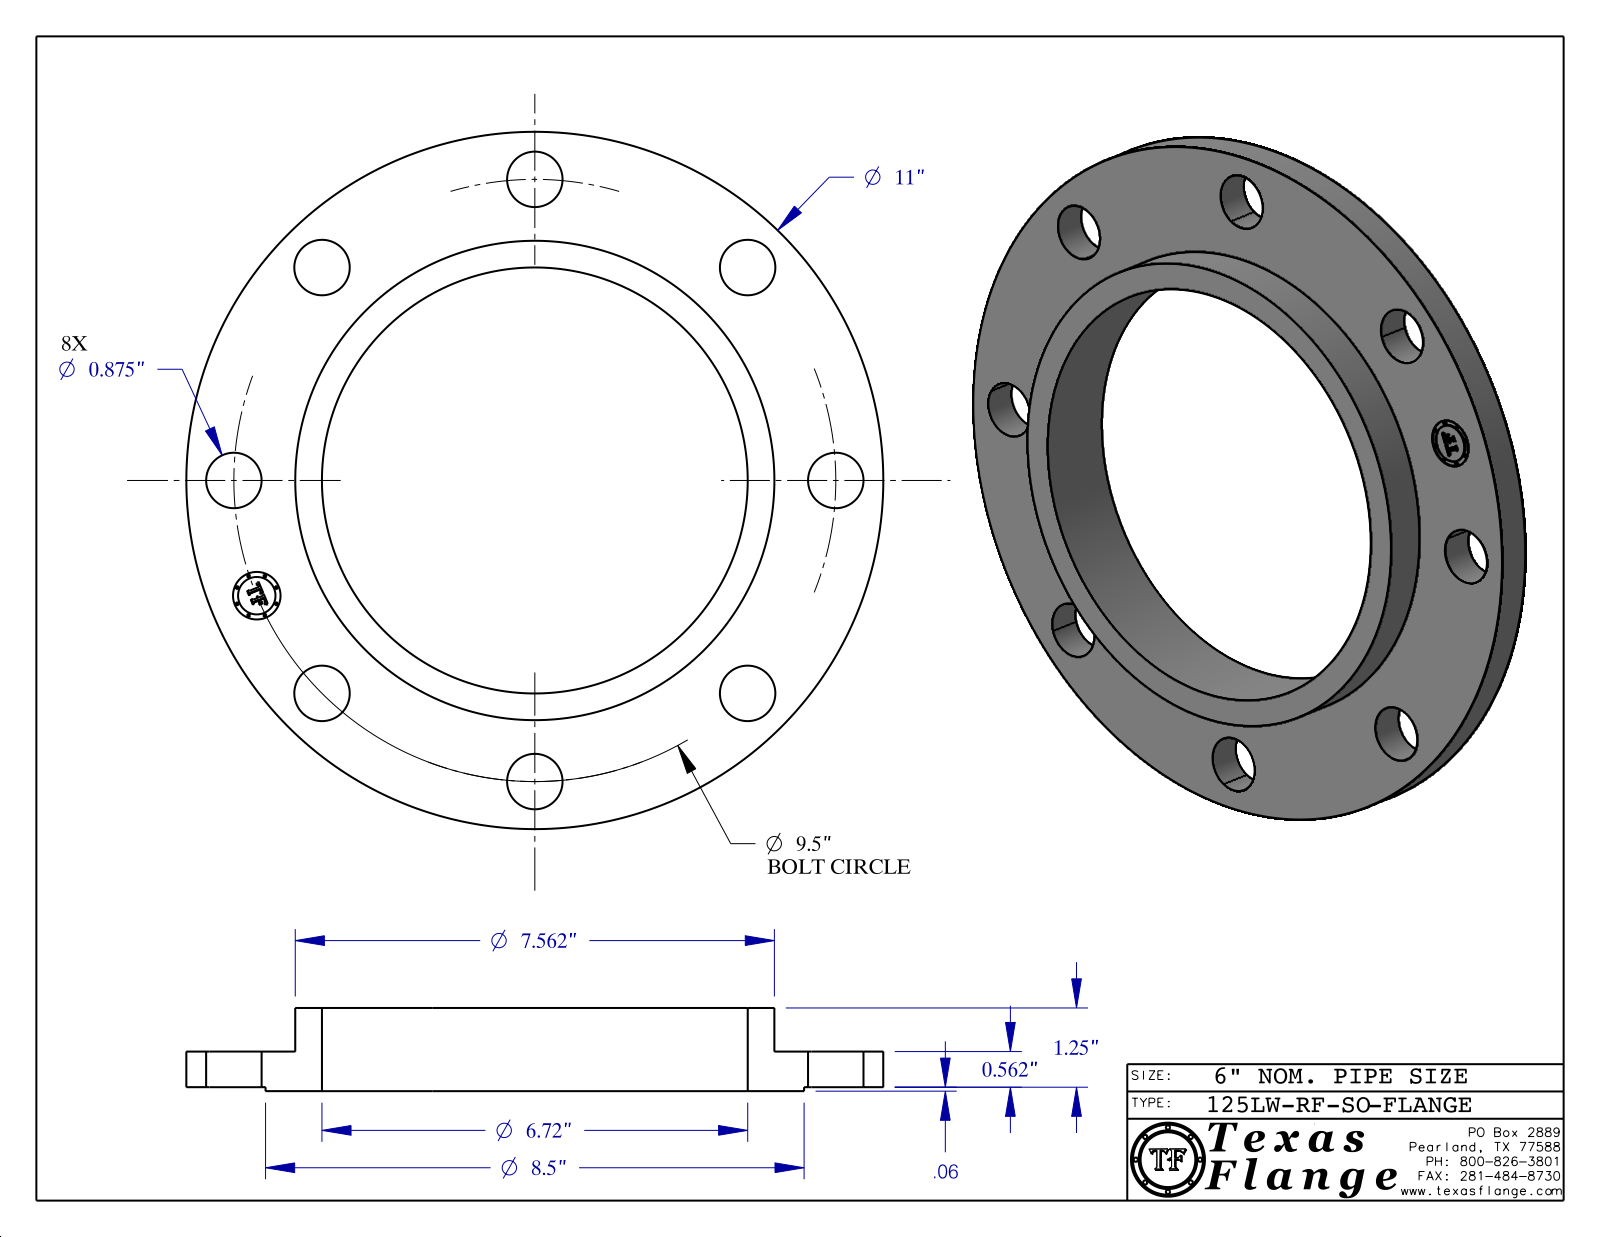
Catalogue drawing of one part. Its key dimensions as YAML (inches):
part_name: "125LW-RF-SO-B16.1"
step_written_by: "CATIA V5 STEP AP214 (AUTOMOTIVE_DESIGN)"
units: inches
bodies: {solids: 1, faces: 413, planar: 369, cylindrical: 44, other: 0}
overall_size: [11, 11, 1.313]
volume: 38.6
surface_area: 187.2
round_holes:
  - {diameter: 0.875, count: 8}
  - {diameter: 0.75, count: 1}
  - {diameter: 6.72, count: 1}
round_bosses_or_shafts:
  - {diameter: 0.045, count: 8}
  - {diameter: 11, count: 1}
  - {diameter: 8.5, count: 1}
  - {diameter: 7.562, count: 1}
  - {diameter: 0.591, count: 1}
face_to_face_distances: [0.562, 0.063, 0.624, 1.313, 1.25, 0.688, 0.609, 0.547, 0.015, 0.703]
hole_center_spacings: [4.75, 3.635, 6.717, 8.777, 5.278, 9.5, 9.5, 1.853]
